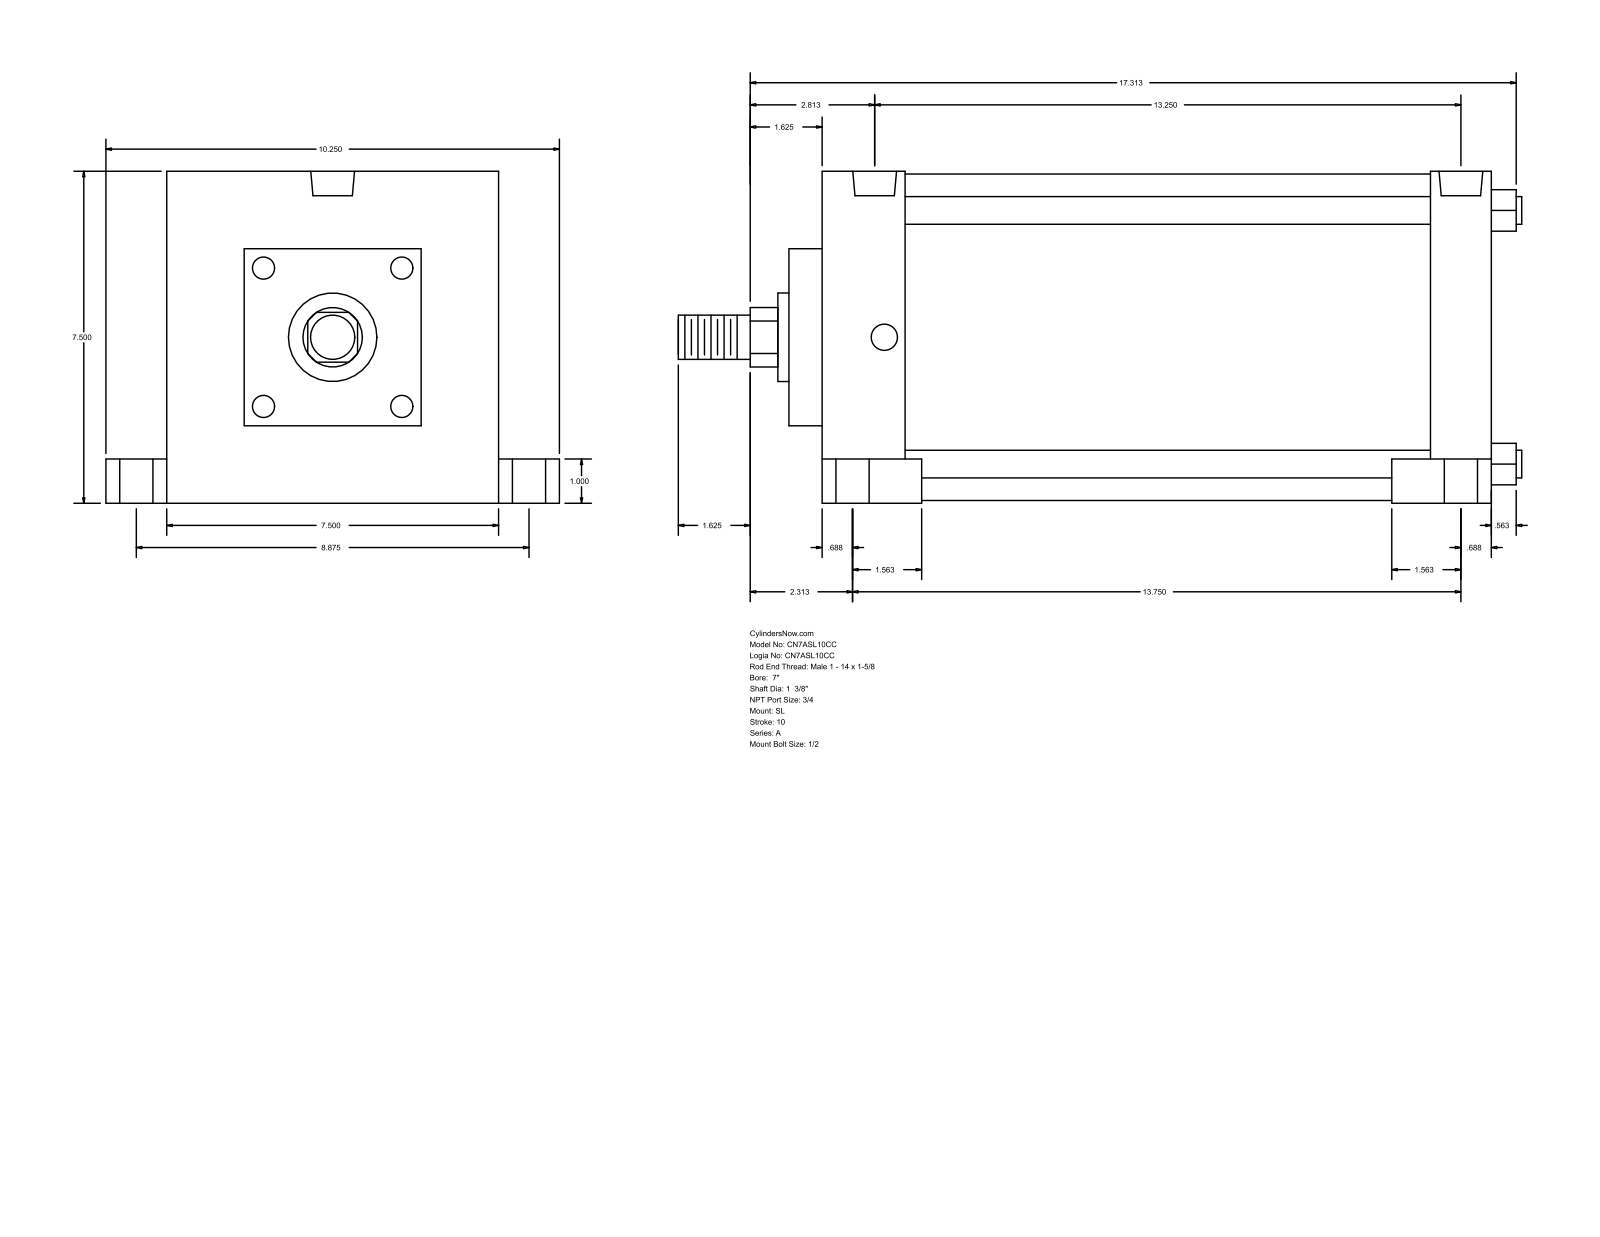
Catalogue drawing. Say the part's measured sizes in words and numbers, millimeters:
The part is named "A_SL__0700_1.375". Its 3-D file was written by "GSSL Pune (CONFIG_CONTROL_DESIGN)". It is 0 solids with 117 faces: 85 planar, 32 cylindrical and 0 other. Overall it measures 484.19 by 260.35 by 190.5 millimeters. Round holes: 4 of diameter 15.08, 4 of diameter 19.05, 4 of diameter 25.4, 2 of diameter 25.12. Round bosses or shafts: 4 of diameter 15.88, 1 of diameter 187.32, 1 of diameter 50.8, 1 of diameter 34.92, 1 of diameter 25.4. Partial cylindrical surfaces (rounded edges, fillets, slot ends): 1 of radius 17.06. The main face-to-face distances are 190.5, 384.18, 34.93, 19.04, 403.22, 66.67, 47.63, 336.55, 368.29, 349.25. The hole center spacings are 5.56, 112.71, 112.85, 113.42, 114.18, 225.42, 325.43, 330.99.
